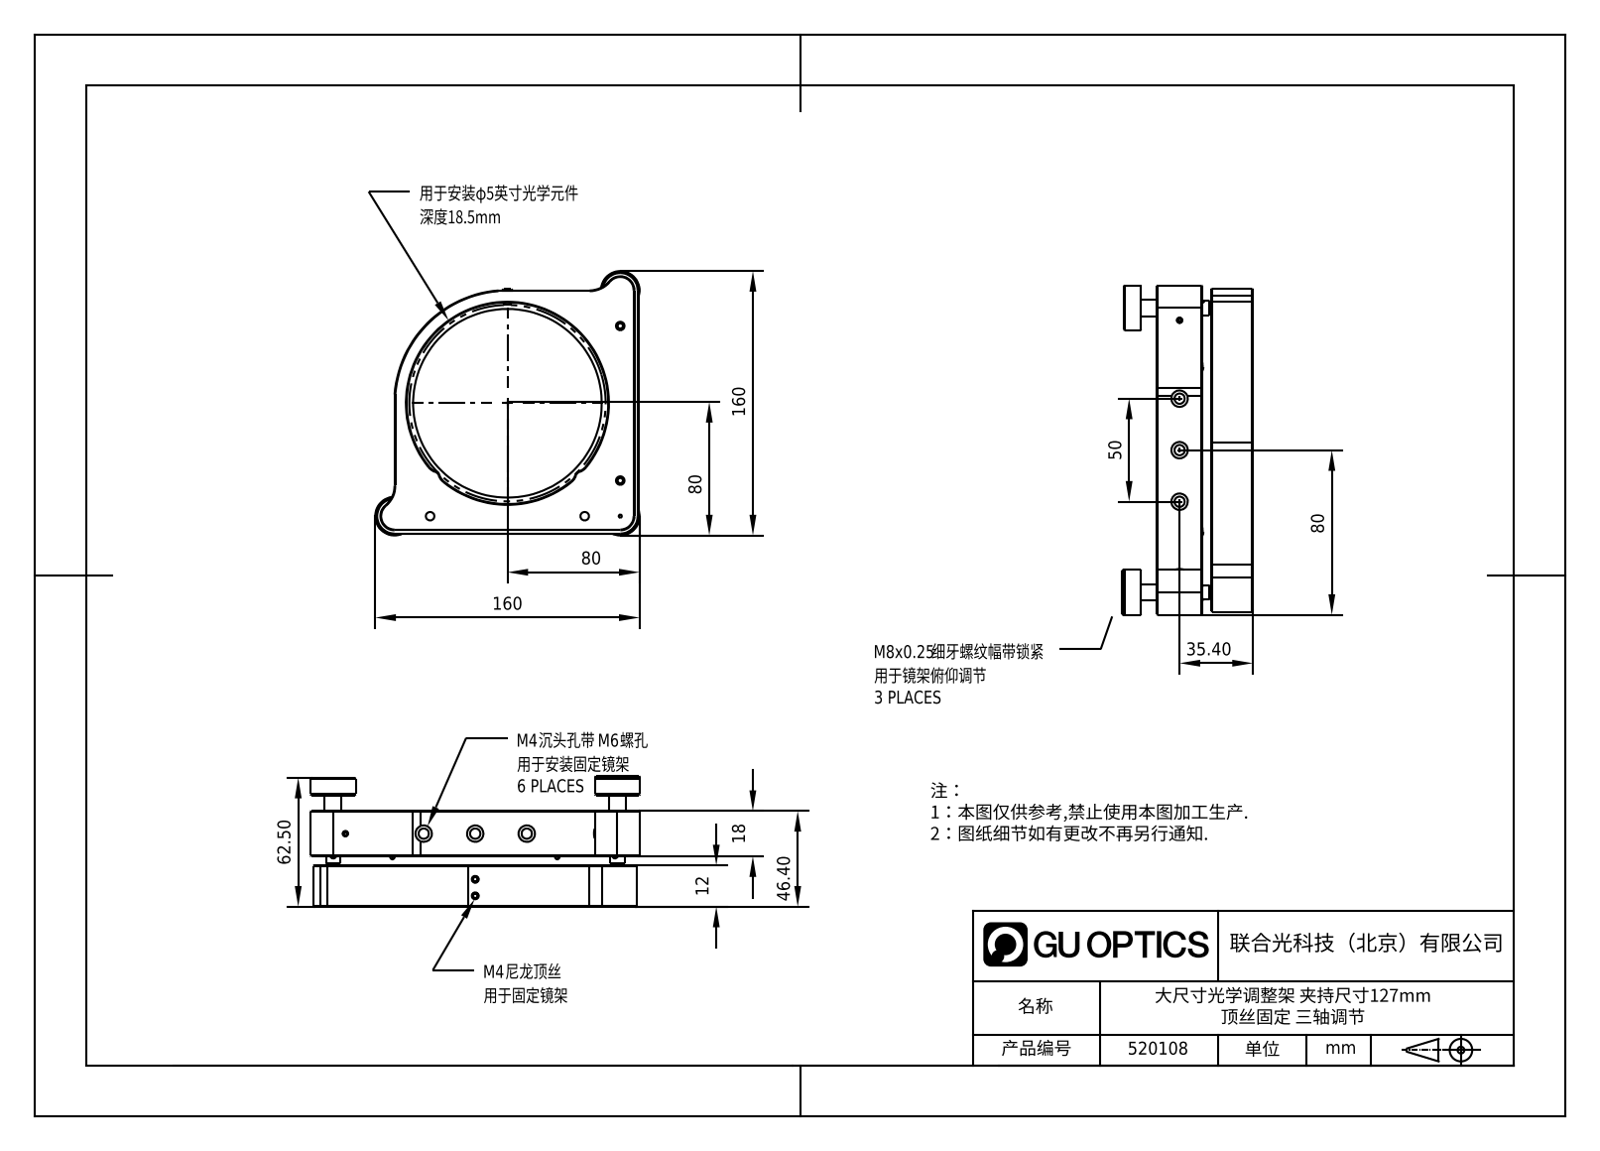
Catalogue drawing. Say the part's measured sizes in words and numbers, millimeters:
The part is named "1.1.1.38_ZJB-5.0-3". Its 3-D file was written by "SolidWorks 2021 (CONFIG_CONTROL_DESIGN)". It is 0 solids with 366 faces: 116 planar, 147 cylindrical and 103 other. Overall it measures 160 by 160 by 63.24 millimeters. Round holes: 10 of diameter 8, 6 of diameter 3.3, 6 of diameter 5, 3 of diameter 3, 3 of diameter 6, 3 of diameter 12, 2 of diameter 1.5, 2 of diameter 2.5, 1 of diameter 13.5, 1 of diameter 125, 1 of diameter 129. Round bosses or shafts: 4 of diameter 2, 3 of diameter 22, 3 of diameter 8, 3 of diameter 7, 2 of diameter 13. Partial cylindrical surfaces (rounded edges, fillets, slot ends): 8 of radius 1.05, 4 of radius 5, 4 of radius 6, 3 of radius 9.5, 2 of radius 2.5, 2 of radius 8, 2 of radius 10, 1 of radius 72. The main face-to-face distances are 20, 22, 4.4, 24.4, 26.4, 46.4, 1.5, 150.41, 151.91, 20.5. The hole center spacings are 25, 97.58, 28, 30, 33.4, 38, 39.17, 50.
